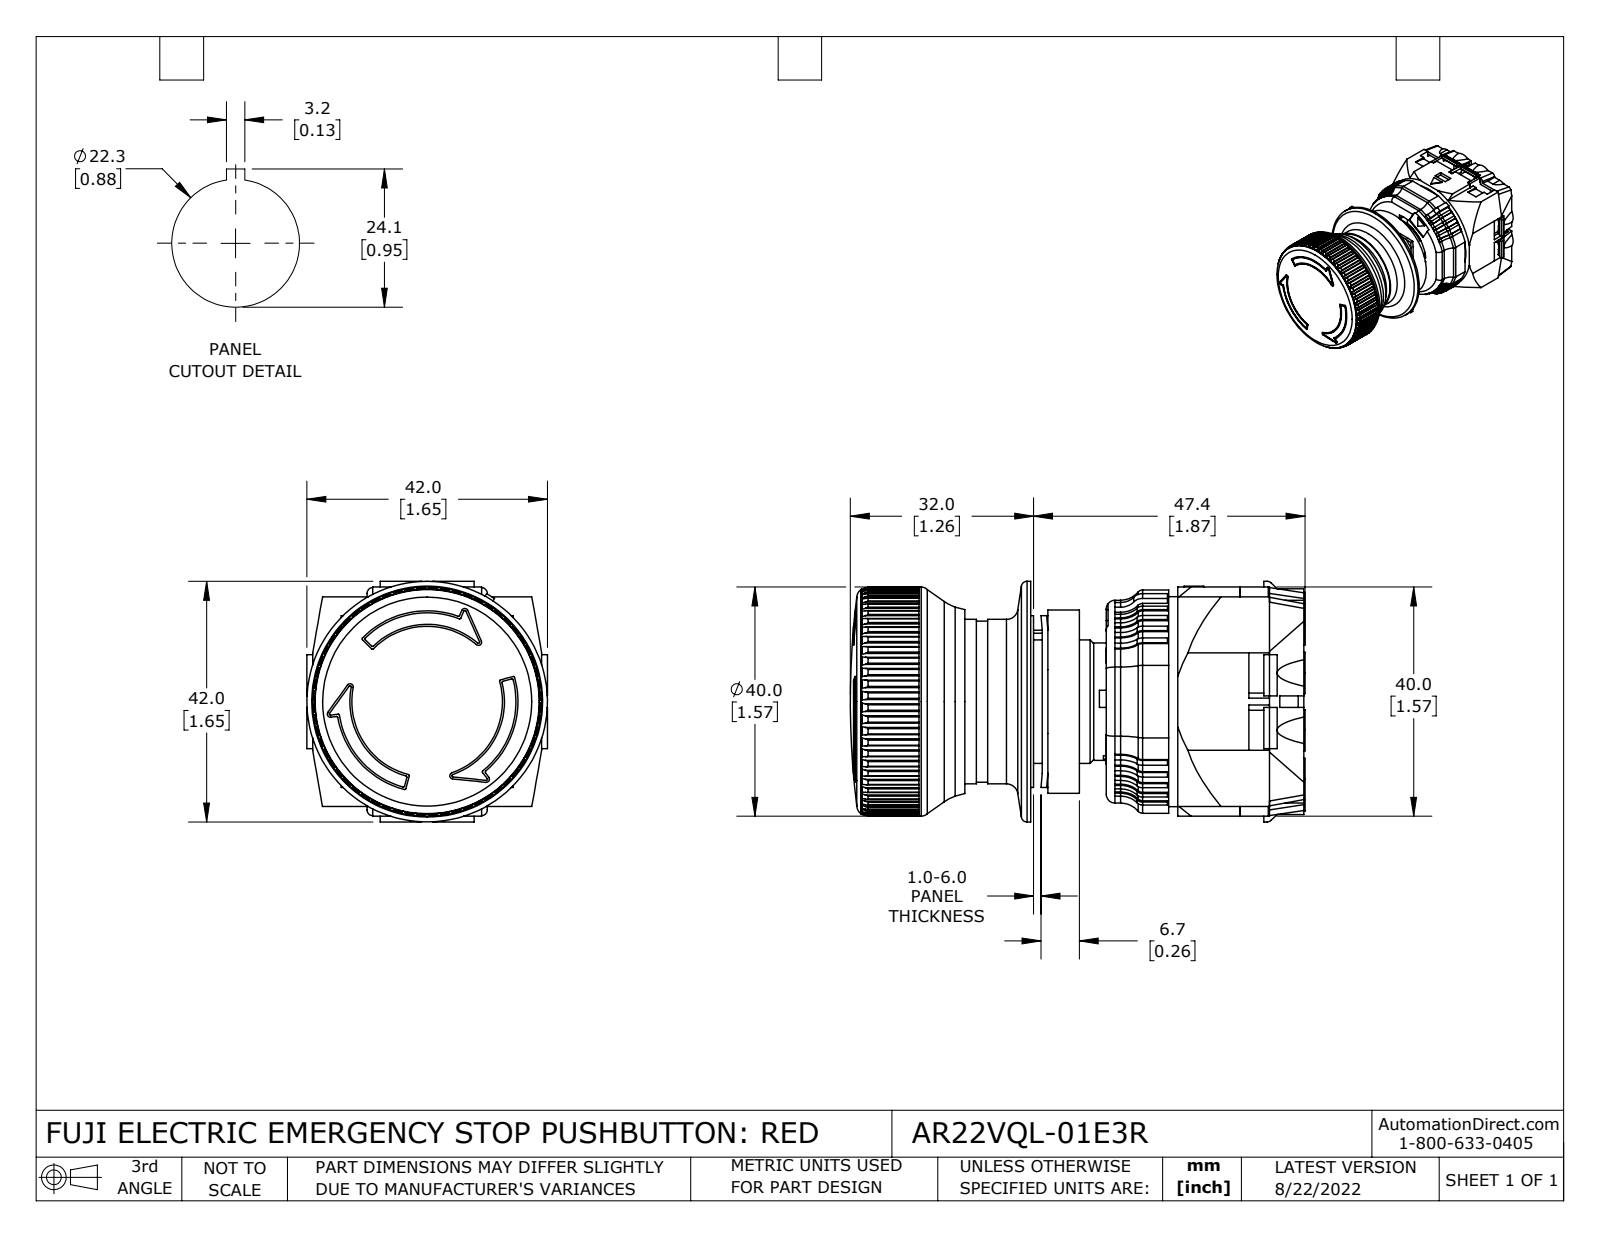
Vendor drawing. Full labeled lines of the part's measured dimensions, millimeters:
Part name (STEP PRODUCT): AR22VQL-01E3R
STEP written by: SolidWorks 2021 (CONFIG_CONTROL_DESIGN)
Units: millimetres
Bodies: 8 solids, 1459 faces (645 planar, 600 cylindrical, 214 other)
Overall size (bounding box): 79.4 × 42 × 42
Volume: 62 430 mm³ · Surface area: 34 710 mm²
Round holes (diameter × count): ⌀3.5 ×12, ⌀6.2 ×12, ⌀8 ×1, ⌀17.5 ×1, ⌀21 ×1, ⌀21.3 ×1, ⌀22 ×1, ⌀22.3 ×1, ⌀28 ×1, ⌀29.7 ×1, ⌀36.7 ×1
Round bosses / shafts (diameter × count): ⌀7.2 ×12, ⌀42 ×1, ⌀40 ×1, ⌀32 ×1, ⌀30 ×1, ⌀28.7 ×1, ⌀28.1 ×1, ⌀22.4 ×1
Partial cylindrical surfaces — rounded edges, fillets, slot ends (radius × count): R0.2 ×146, R0.4 ×64, R1.2 ×19, R3.8 ×19, R4.2 ×12, R1 ×10, R0.6 ×6, R1.5 ×4
Main face-to-face distances: 1, 18.5, 11.5, 10, 44.7, 18, 21, 3, 23.6, 4
Hole centre spacings: 16.3, 23, 8.3, 8.9, 10, 14.9, 18.1, 18.7
